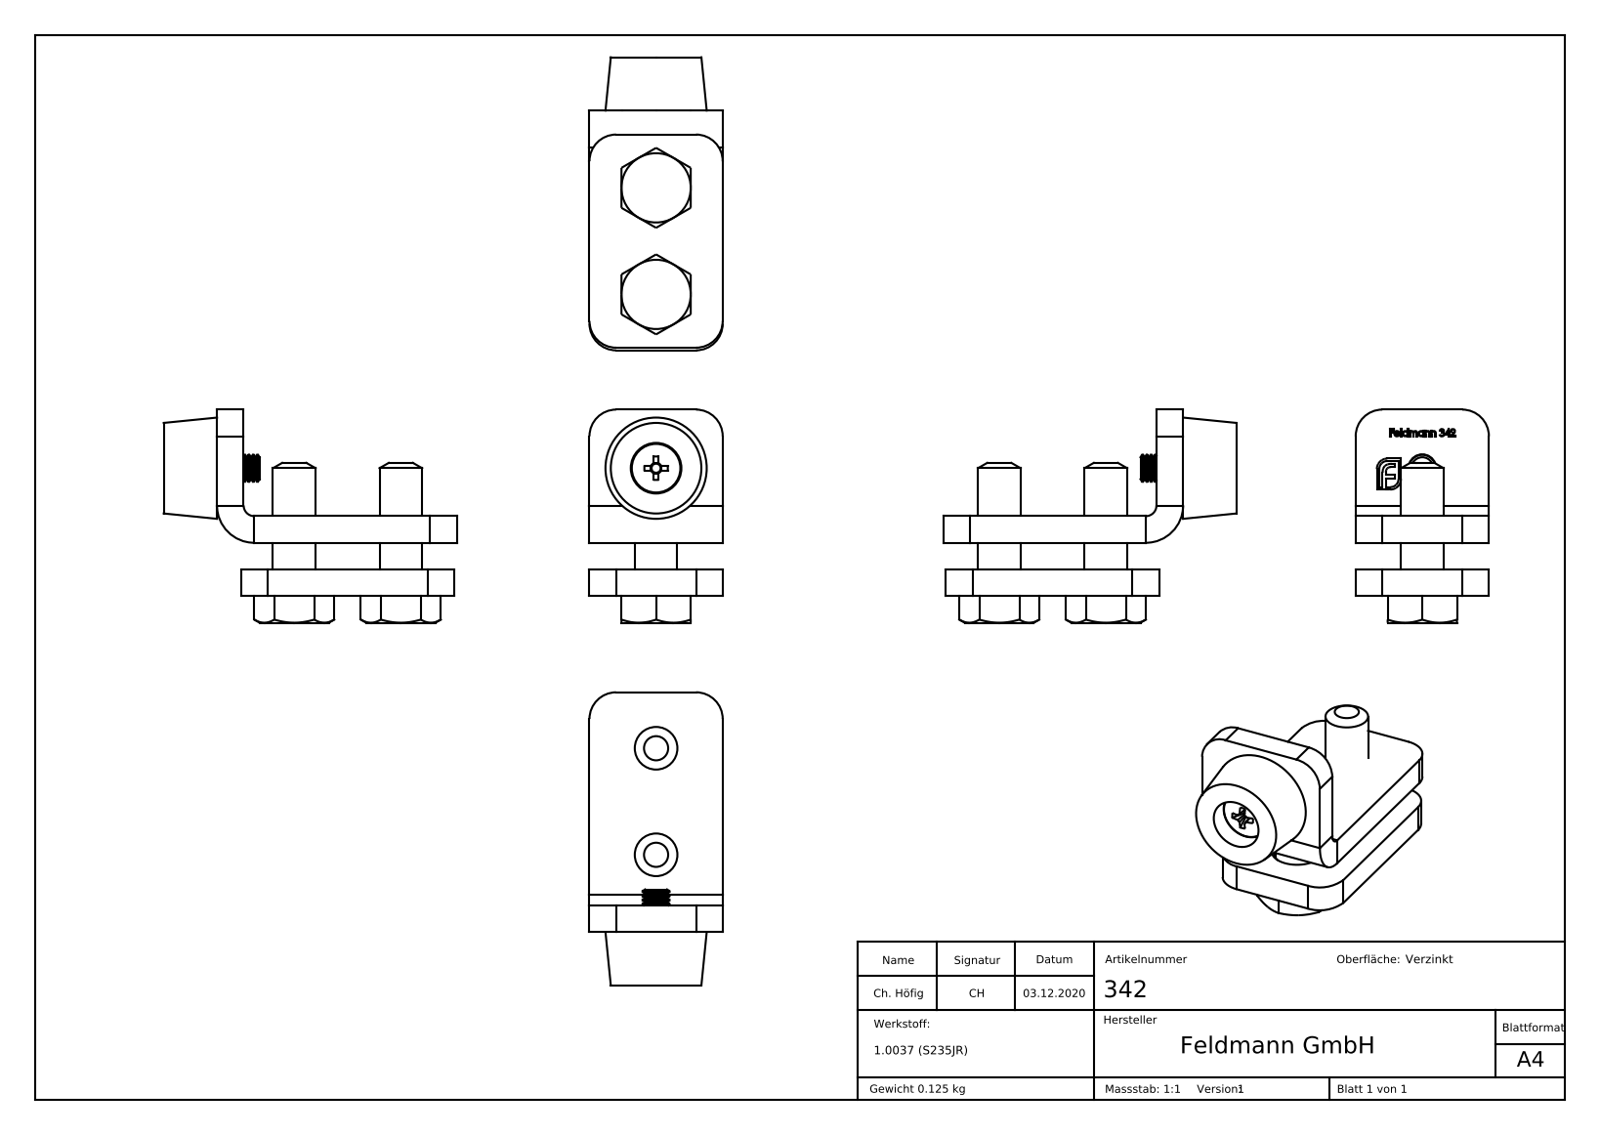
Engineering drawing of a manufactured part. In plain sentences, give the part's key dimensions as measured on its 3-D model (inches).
The part is named "342 Teil1_342 Teil1; DIN 931_DIN 931 M8x25; 342 Teil2_342 Teil2; DIN 931 (+7 more)". Its 3-D file was written by "SolidWorks 2018 (CONFIG_CONTROL_DESIGN)". It is 6 solids with 419 faces: 169 planar, 58 cylindrical and 192 other. Overall it measures 1259.843 by 411.754 by 403.667 inches. Its volume is 1.1 cubic inches and its surface area 16.47 square inches. Round holes: 2 of diameter 0.268, 2 of diameter 0.335, 1 of diameter 0.165, 1 of diameter 0.374. Round bosses or shafts: 2 of diameter 0.315, 1 of diameter 0.197. Partial cylindrical surfaces (rounded edges, fillets, slot ends): 8 of radius 0.197, 1 of radius 0.079, 1 of radius 0.276. The main face-to-face distances are 0.197, 0.394, 0.591, 0.984, 0.787, 0.236, 1.575, 0.512, 0.02, 0.748. The hole center spacings are 0.787.
